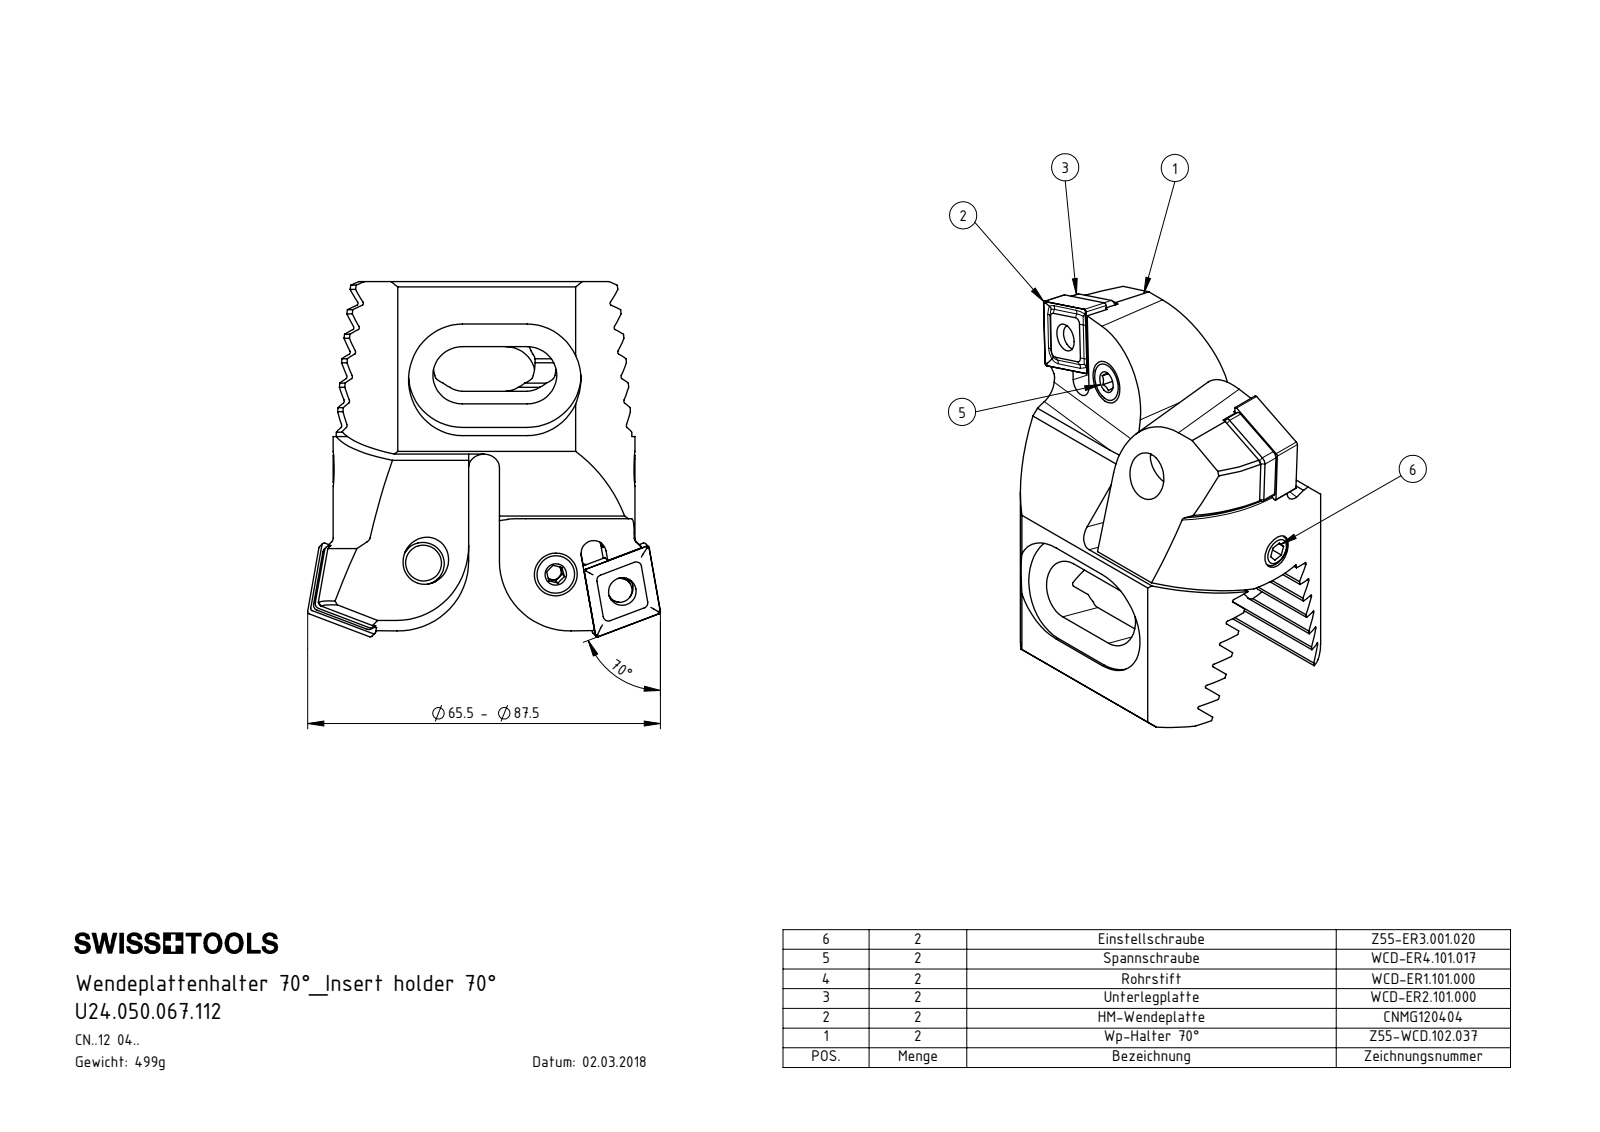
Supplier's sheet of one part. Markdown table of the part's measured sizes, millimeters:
| quantity | value |
| --- | --- |
| part name | WCD-ER3.101.000_A; Z55-ER3.001.020; WCD-ER4.101.017_A; Z55-WCD.102.037_A (+5 more) |
| STEP written by | SolidWorks 2017 (AUTOMOTIVE_DESIGN) |
| units | millimeters |
| bodies | 14 solids, 470 faces (244 planar, 108 cylindrical, 118 other) |
| overall size | 65.92 × 65.5 × 44 |
| volume | 62 759 mm³ |
| surface area | 26 356 mm² |
| round holes (diameter × count) | 1 × 2, 5.16 × 2, 6.4 × 2, 7 × 2, 8.4 × 2, 5 × 1 |
| round bosses / shafts (diameter × count) | 8 × 2, 7.9 × 2, 6.4 × 2, 4.5 × 2, 3.55 × 2, 6 × 1, 4 × 1 |
| partial cylindrical surfaces (radius × count) | 0.34 × 12, 1 × 10, 0.4 × 8, 2.5 × 6, 3 × 4, 5.5 × 4, 10 × 4, 2.1 × 2 |
| main face-to-face distances | 4.07, 8.14, 12.21, 16.28, 20.35, 1, 7.12, 44, 4.46, 28.75 |
| hole center spacings | 12.8, 15, 12.85, 12.86, 28.98 |
